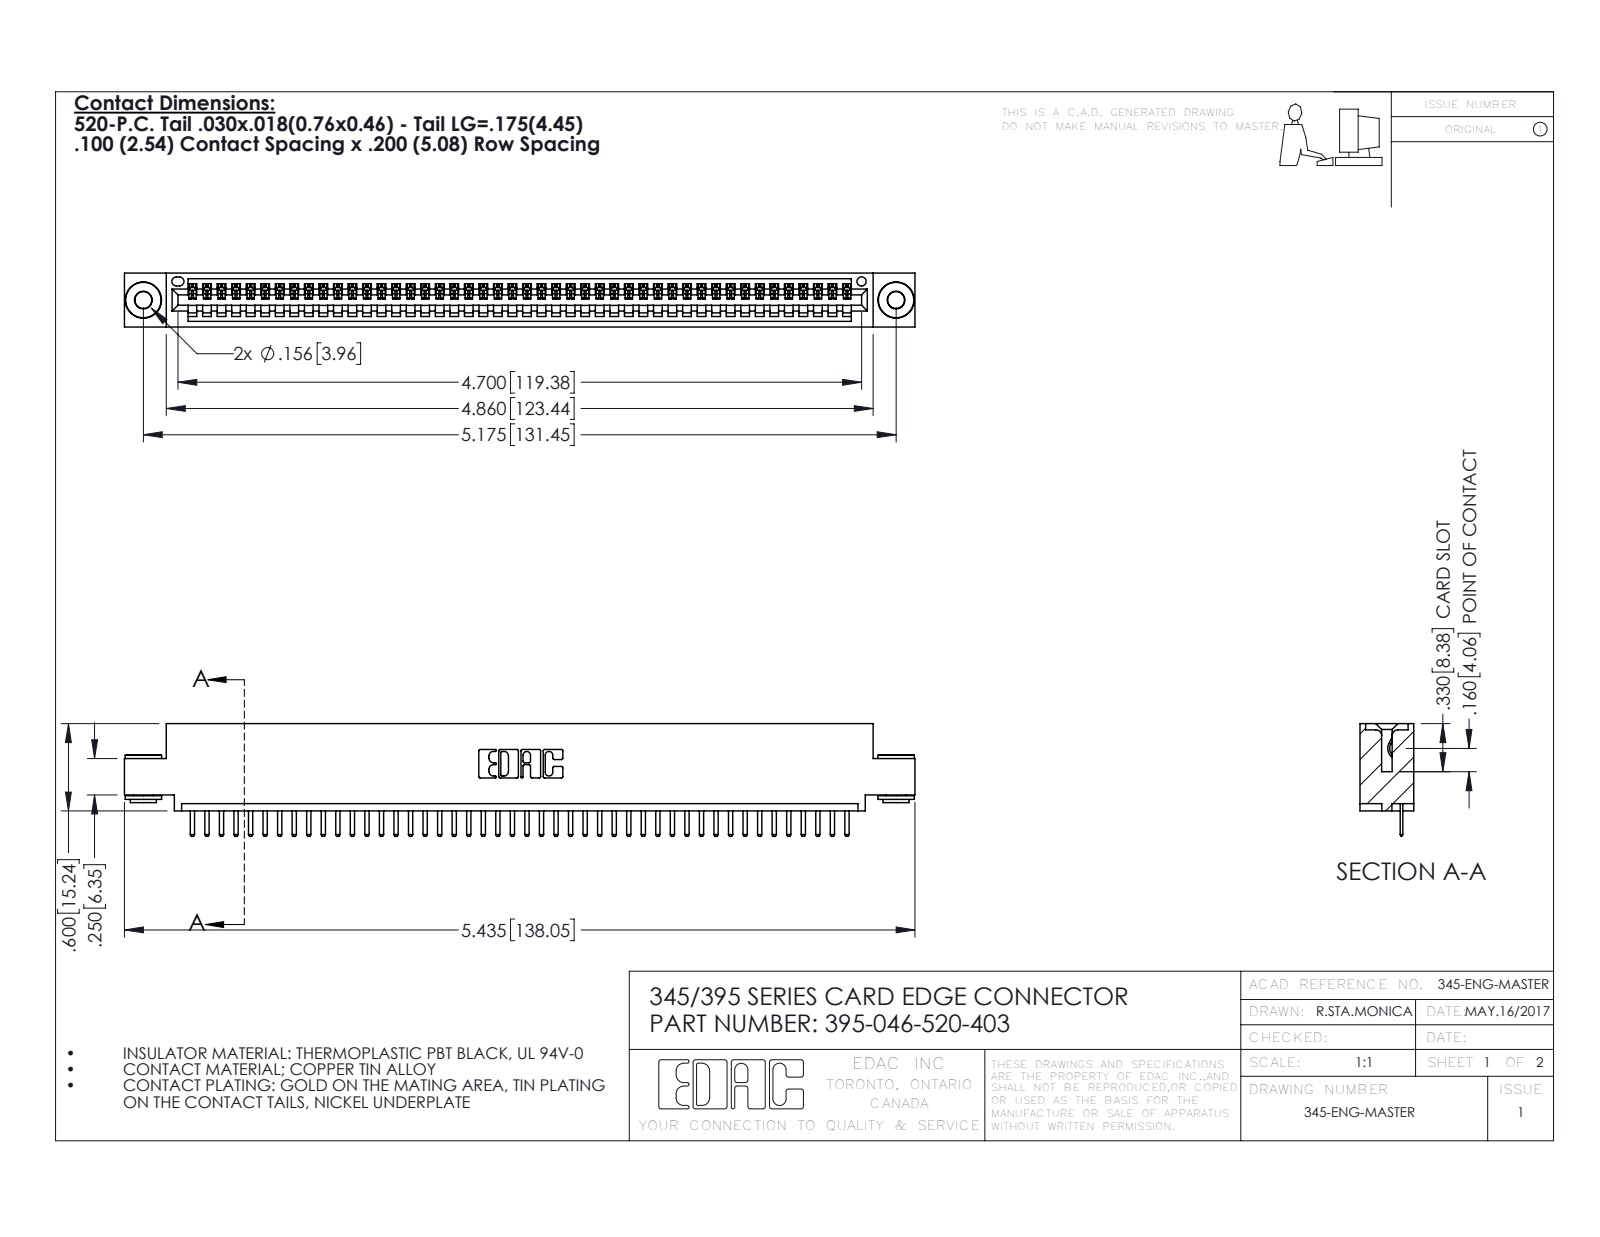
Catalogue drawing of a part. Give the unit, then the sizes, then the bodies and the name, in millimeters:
Units: millimetres
Overall size (bounding box): 138 × 19.7 × 9.4
Round holes (diameter × count): ⌀2.9 ×2, ⌀4 ×2, ⌀1.6 ×1
Round bosses / shafts (diameter × count): ⌀6.4 ×2, ⌀4.6 ×2, ⌀3.5 ×2
Partial cylindrical surfaces — rounded edges, fillets, slot ends (radius × count): R0.3 ×94, R0.2 ×92, R0.3 ×22, R0.2 ×6, R0.8 ×6, R0.7 ×3, R0.8 ×2, R1 ×2
Main face-to-face distances: 1.8, 7.6, 9.4, 5.1, 0.6, 2.5, 6.9, 5.7, 1.8, 3.8
Hole centre spacings: 6.9, 125.5, 131.4
Volume: 13 000 mm³ · Surface area: 17 140 mm²
Bodies: 49 solids, 3020 faces (2026 planar, 986 cylindrical, 8 other)
Part name (STEP PRODUCT): 345-292-001_345-293-120; 395-046-520-403; 345-250-002_345-250-002-102; 345 Part_0.110 Offset - 0.156 Dia-TH
STEP written by: SolidWorks 2016 (CONFIG_CONTROL_DESIGN)
